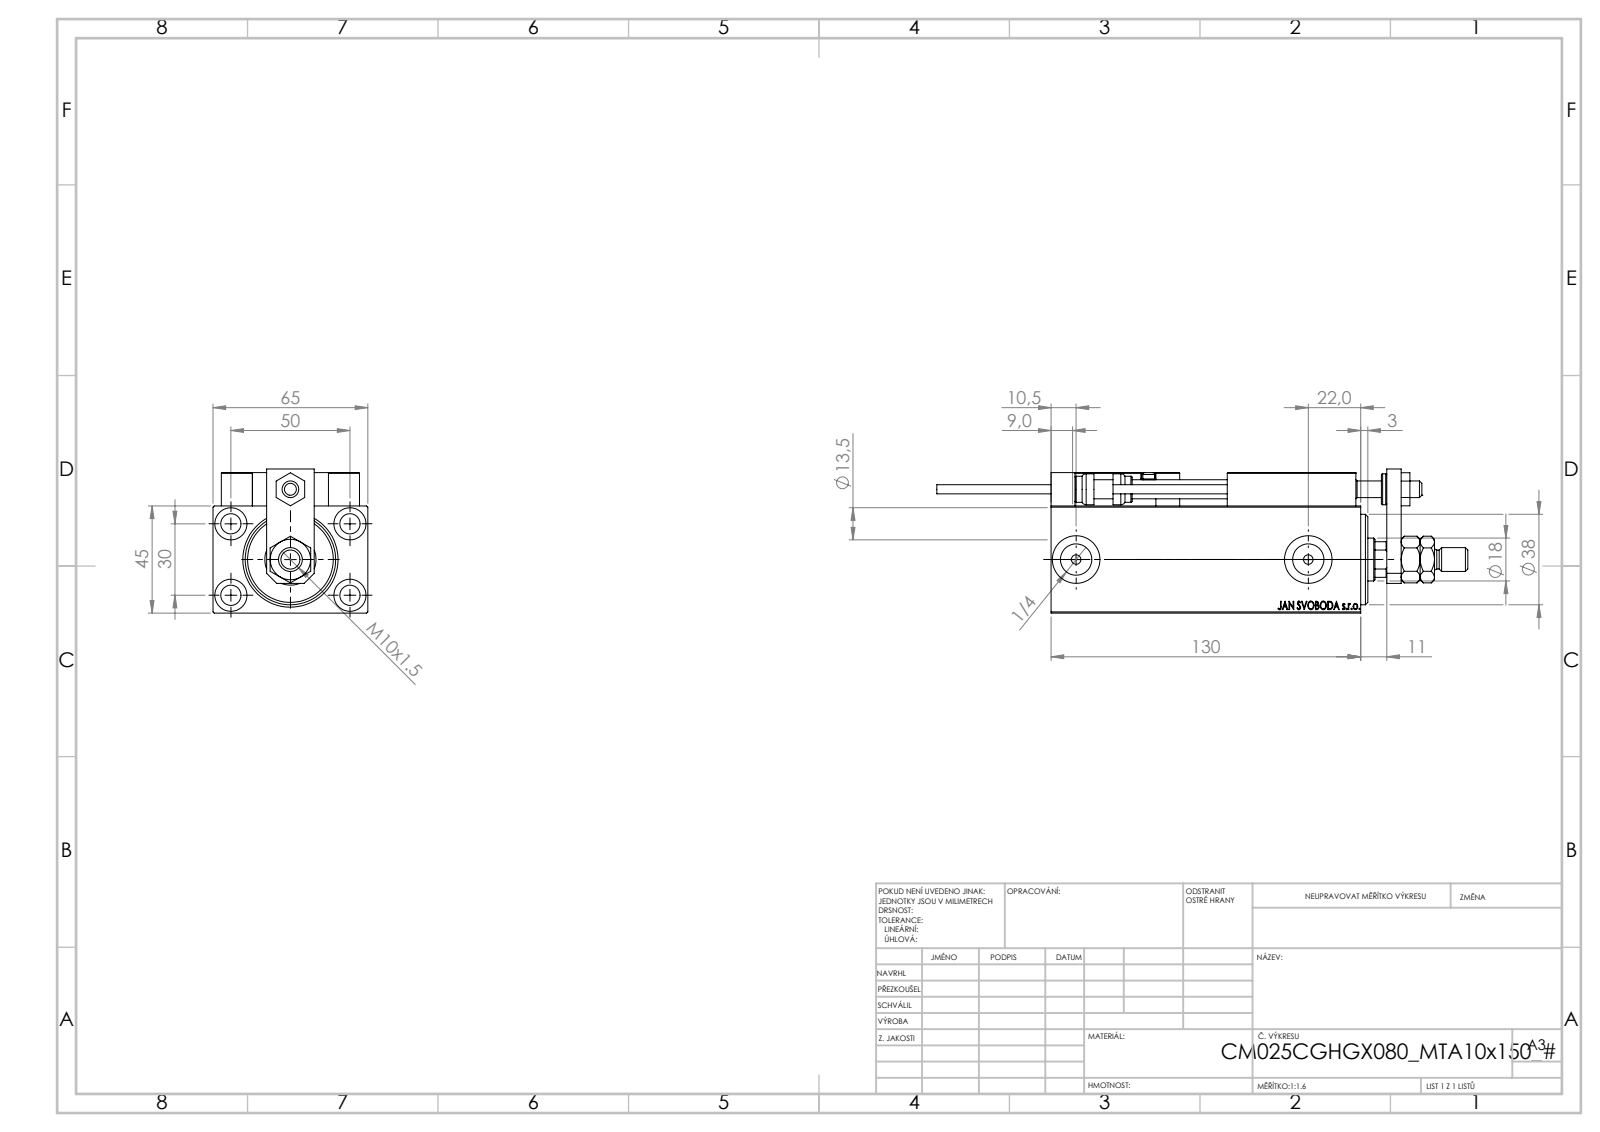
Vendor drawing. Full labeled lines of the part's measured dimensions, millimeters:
Part name (STEP PRODUCT): KONCOVKA; X_Y_MTA; SWITCH_X_FRONT_BACK; NUT_D12 (+8 more)
STEP written by: SolidWorks 2019 (CONFIG_CONTROL_DESIGN)
Units: millimetres
Bodies: 24 solids, 1331 faces (575 planar, 192 cylindrical, 564 other)
Overall size (bounding box): 223 × 65 × 60.5
Volume: 378 292 mm³ · Surface area: 101 651 mm²
Round holes (diameter × count): ⌀4 ×6, ⌀8 ×5, ⌀8.5 ×5, ⌀3.2 ×4, ⌀13.5 ×4, ⌀5 ×2, ⌀13.16 ×2, ⌀20 ×2, ⌀7 ×1, ⌀14.5 ×1, ⌀18 ×1, ⌀21.5 ×1
Round bosses / shafts (diameter × count): ⌀5 ×2, ⌀3.8 ×2, ⌀13 ×1, ⌀11 ×1, ⌀10 ×1, ⌀8 ×1
Partial cylindrical surfaces — rounded edges, fillets, slot ends (radius × count): R0.3 ×30, R3 ×2, R8.5 ×1
Main face-to-face distances: 45, 65, 14, 6, 59, 3, 13, 20, 141, 3.5
Hole centre spacings: 29.15, 11.37, 20, 28.9, 29.59, 29.69, 30, 36.06
